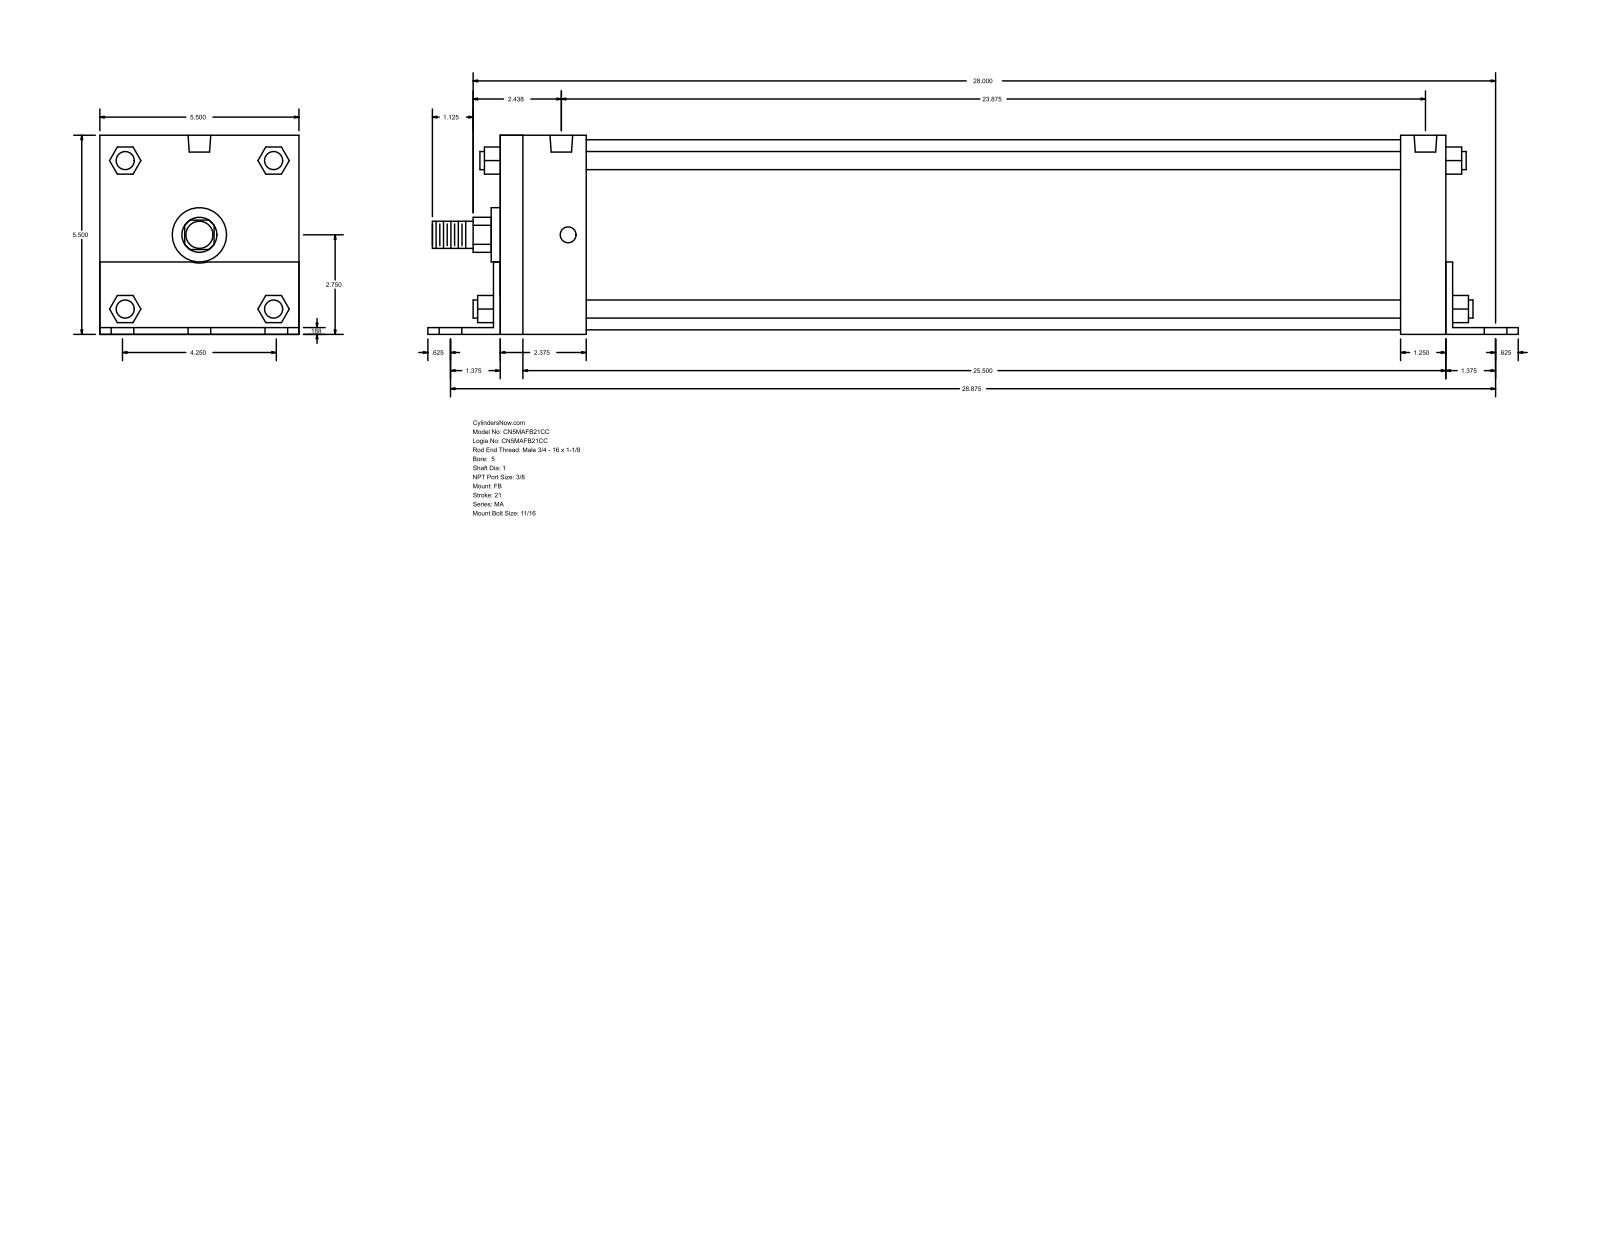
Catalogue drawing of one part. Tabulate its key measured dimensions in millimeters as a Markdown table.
| quantity | value |
| --- | --- |
| part name | MA_FB__0500_1 |
| STEP written by | GSSL Pune (CONFIG_CONTROL_DESIGN) |
| units | millimeters |
| bodies | 0 solids, 140 faces (105 planar, 35 cylindrical, 0 other) |
| overall size | 765.17 × 139.75 × 139.7 |
| round holes (diameter × count) | 17.46 × 6, 11.11 × 4, 15.93 × 2 |
| round bosses / shafts (diameter × count) | 12.7 × 4, 133.35 × 1, 38.1 × 1, 25.4 × 1, 19.05 × 1 |
| partial cylindrical surfaces (radius × count) | 12.29 × 1, 19.81 × 1 |
| main face-to-face distances | 139.7, 4.76, 139.75, 4.71, 134.99, 663.57, 4.77, 36.51, 668.34, 668.33 |
| hole center spacings | 53.98, 735.41, 733.43, 4.76, 73.04, 76.33, 94.68, 98.63 |
